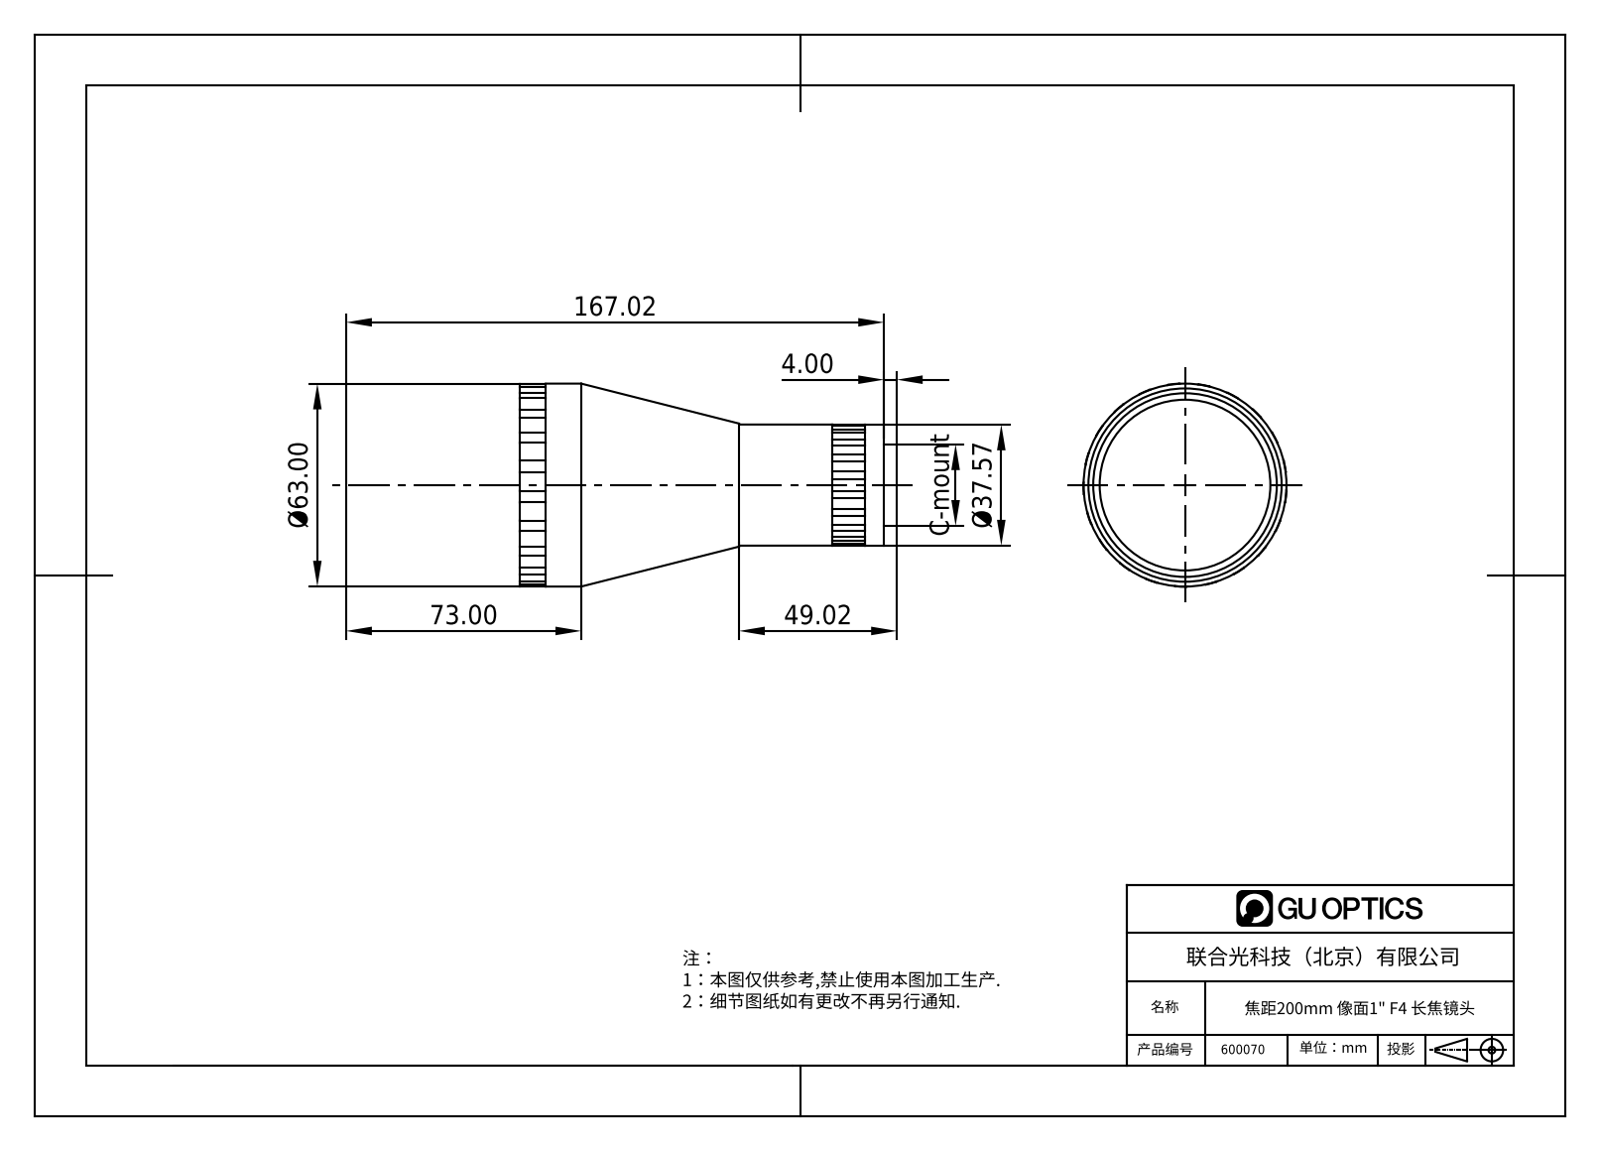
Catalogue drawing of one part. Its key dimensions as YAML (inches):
part_name: "600070"
step_written_by: "SolidWorks 2020 (CONFIG_CONTROL_DESIGN)"
units: inches
bodies: {solids: 9, faces: 154, planar: 36, cylindrical: 104, other: 14}
overall_size: [7.265, 2.481, 2.481]
volume: 22.5
surface_area: 114.2
round_holes:
  - {diameter: 0.878, count: 1}
  - {diameter: 1.205, count: 1}
  - {diameter: 1.396, count: 1}
  - {diameter: 2.008, count: 1}
  - {diameter: 2.264, count: 1}
  - {diameter: 2.348, count: 1}
  - {diameter: 2.362, count: 1}
round_bosses_or_shafts:
  - {diameter: 2.48, count: 1}
  - {diameter: 2.165, count: 1}
  - {diameter: 2.087, count: 1}
  - {diameter: 1.479, count: 1}
  - {diameter: 1.181, count: 1}
  - {diameter: 1, count: 1}
  - {diameter: 0.969, count: 1}
  - {diameter: 0.717, count: 1}
partial_cylinders:
  - {radius: 0.295, count: 20}
  - {radius: 0.413, count: 20}
  - {radius: 1.24, count: 1}
face_to_face_distances: [1.188, 1.739, 0.551, 0.118, 1.306, 1.857, 2.172, 2.054, 0.866, 0.315]
